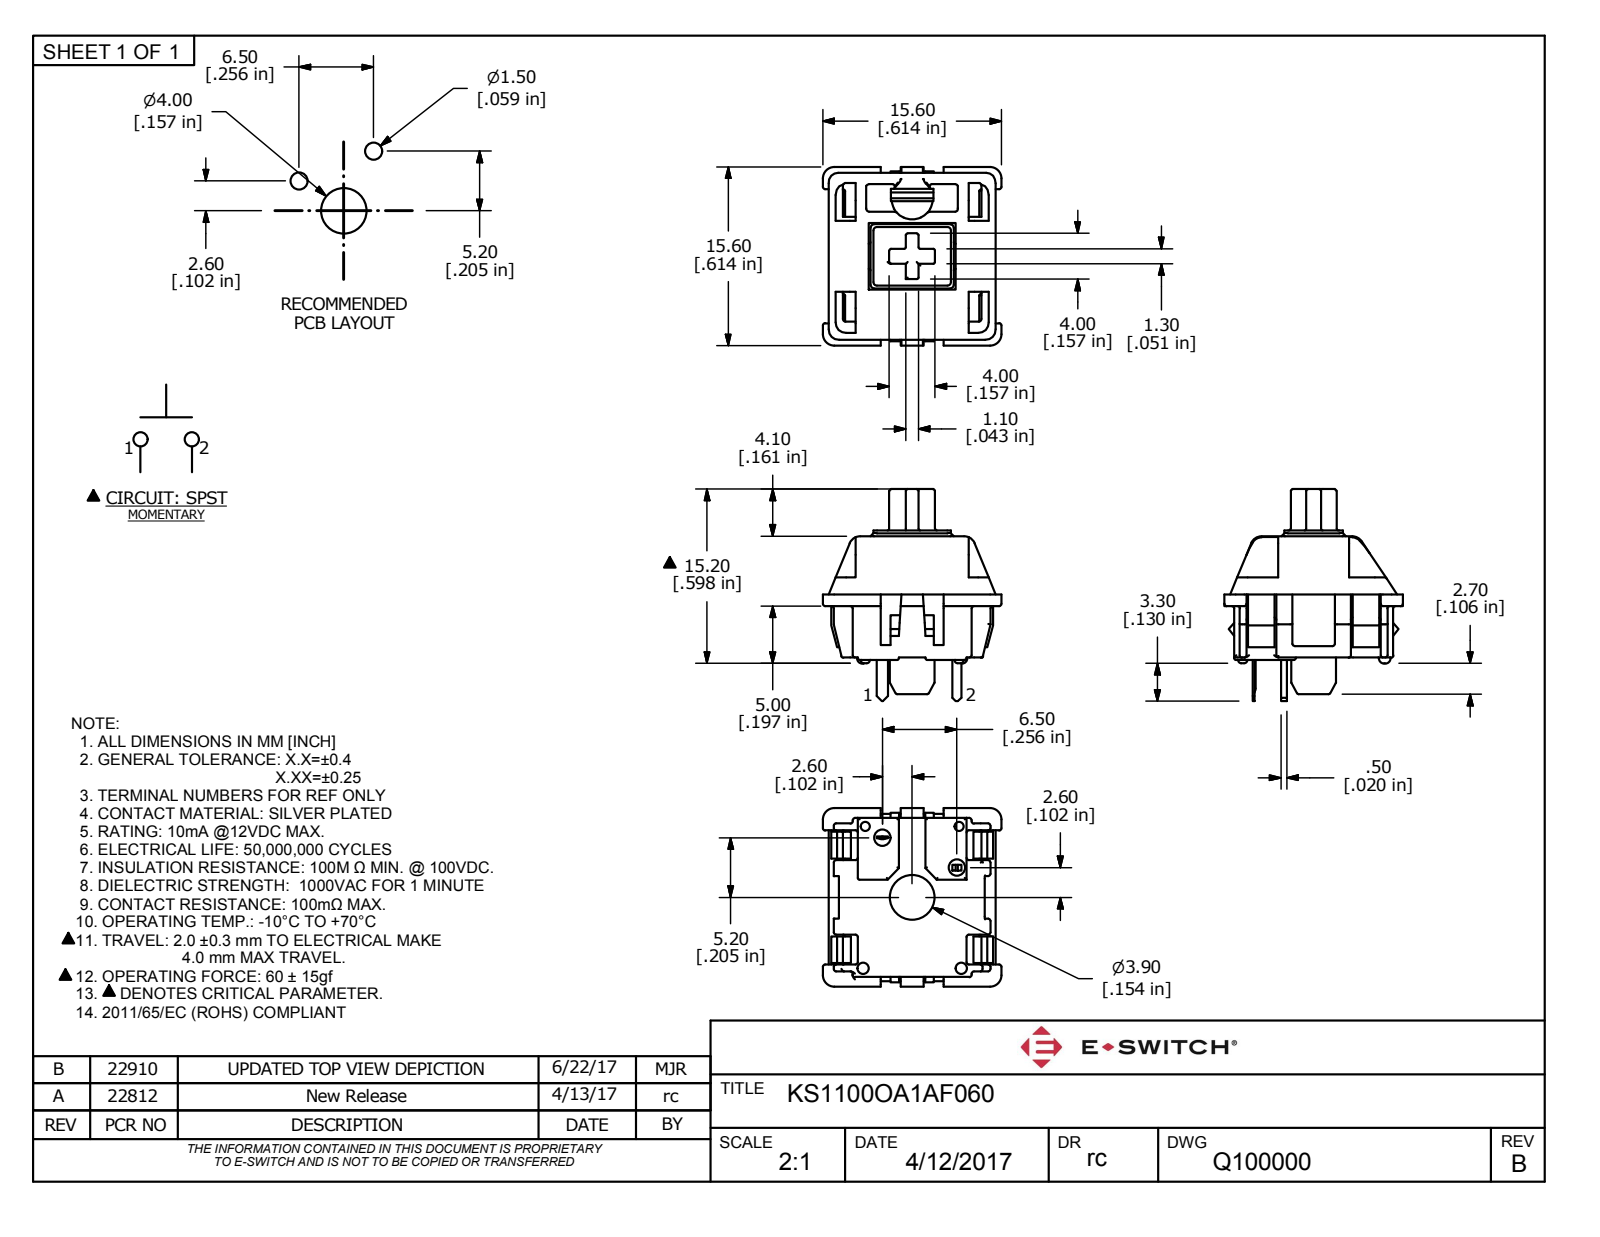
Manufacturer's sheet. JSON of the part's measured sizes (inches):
{"part_name": "P:\\\\E-Switch Secure\\\\3D_MODELS_STP_FORMAT\\\\KS1100OA1AF060.stp", "step_written_by": "ACIS (CONFIG_CONTROL_DESIGN)", "units": "inches", "bodies": {"solids": 1, "faces": 632, "planar": 286, "cylindrical": 239, "other": 107}, "overall_size": [0.728, 0.614, 0.614], "volume_in3": 0.057, "surface_area_in2": 3.258, "round_holes": [[0.055, 2]], "round_bosses_or_shafts": [[0.039, 2], [0.031, 2], [0.154, 1]], "partial_cylinders_radius": [[0.008, 98], [0.006, 38], [0.01, 20], [0.012, 12], [0.039, 12], [0.016, 3], [0.071, 1]], "face_to_face_distances": [0.039, 0.043, 0.035, 0.388, 0.217, 0.028, 0.189, 0.138, 0.022, 0.38], "hole_center_spacings": [0.276]}
